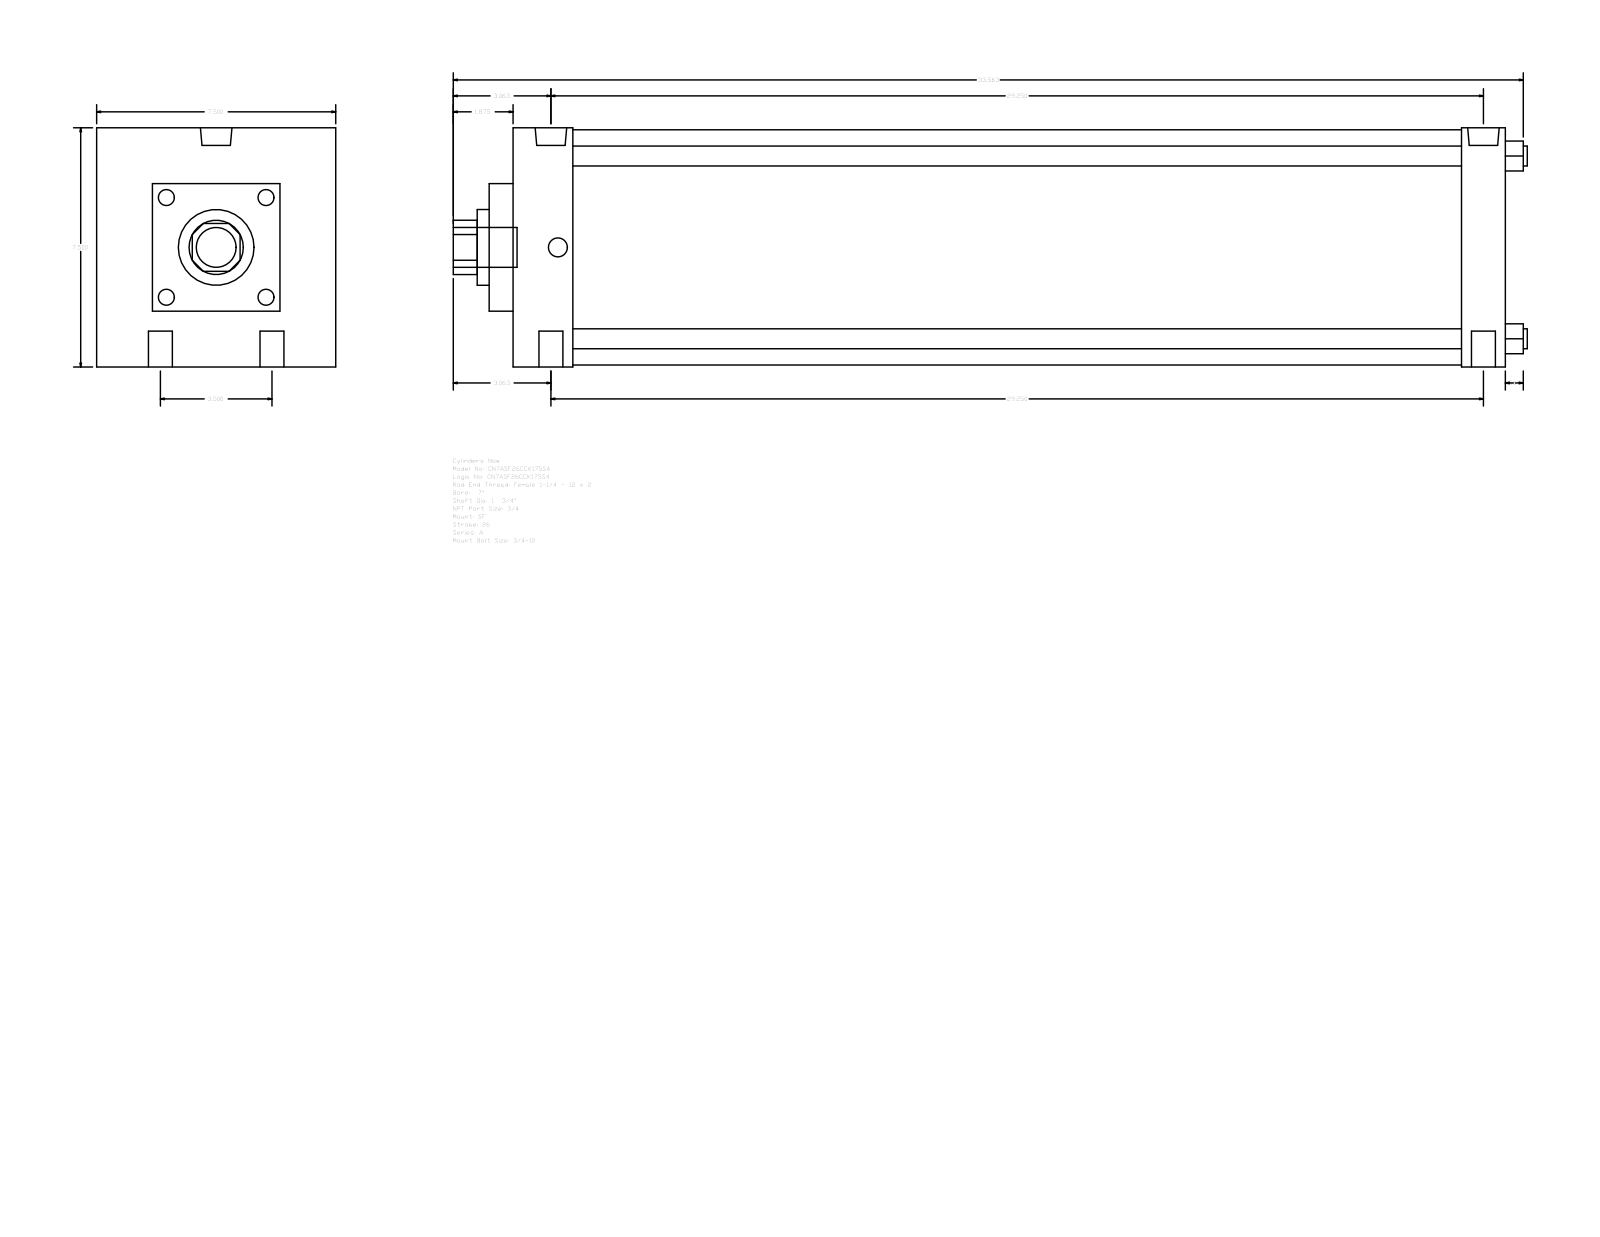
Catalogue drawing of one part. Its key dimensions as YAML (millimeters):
part_name: "A_SF__0700_1.75"
step_written_by: "GSSL Pune (CONFIG_CONTROL_DESIGN)"
units: millimeters
bodies: {solids: 0, faces: 93, planar: 67, cylindrical: 26, other: 0}
overall_size: [855.66, 190.5, 190.5]
round_holes:
  - {diameter: 19.05, count: 4}
  - {diameter: 15.08, count: 2}
  - {diameter: 25.12, count: 2}
  - {diameter: 44.45, count: 1}
  - {diameter: 60.33, count: 1}
round_bosses_or_shafts:
  - {diameter: 15.88, count: 4}
  - {diameter: 187.32, count: 1}
  - {diameter: 31.75, count: 1}
partial_cylinders:
  - {radius: 21.63, count: 1}
face_to_face_distances: [190.5, 790.58, 44.45, 19.05, 47.63, 755.65, 708.02, 742.95, 34.93, 146.05]
hole_center_spacings: [44.45, 744.28, 742.95, 88.9, 748.25, 731.83]
